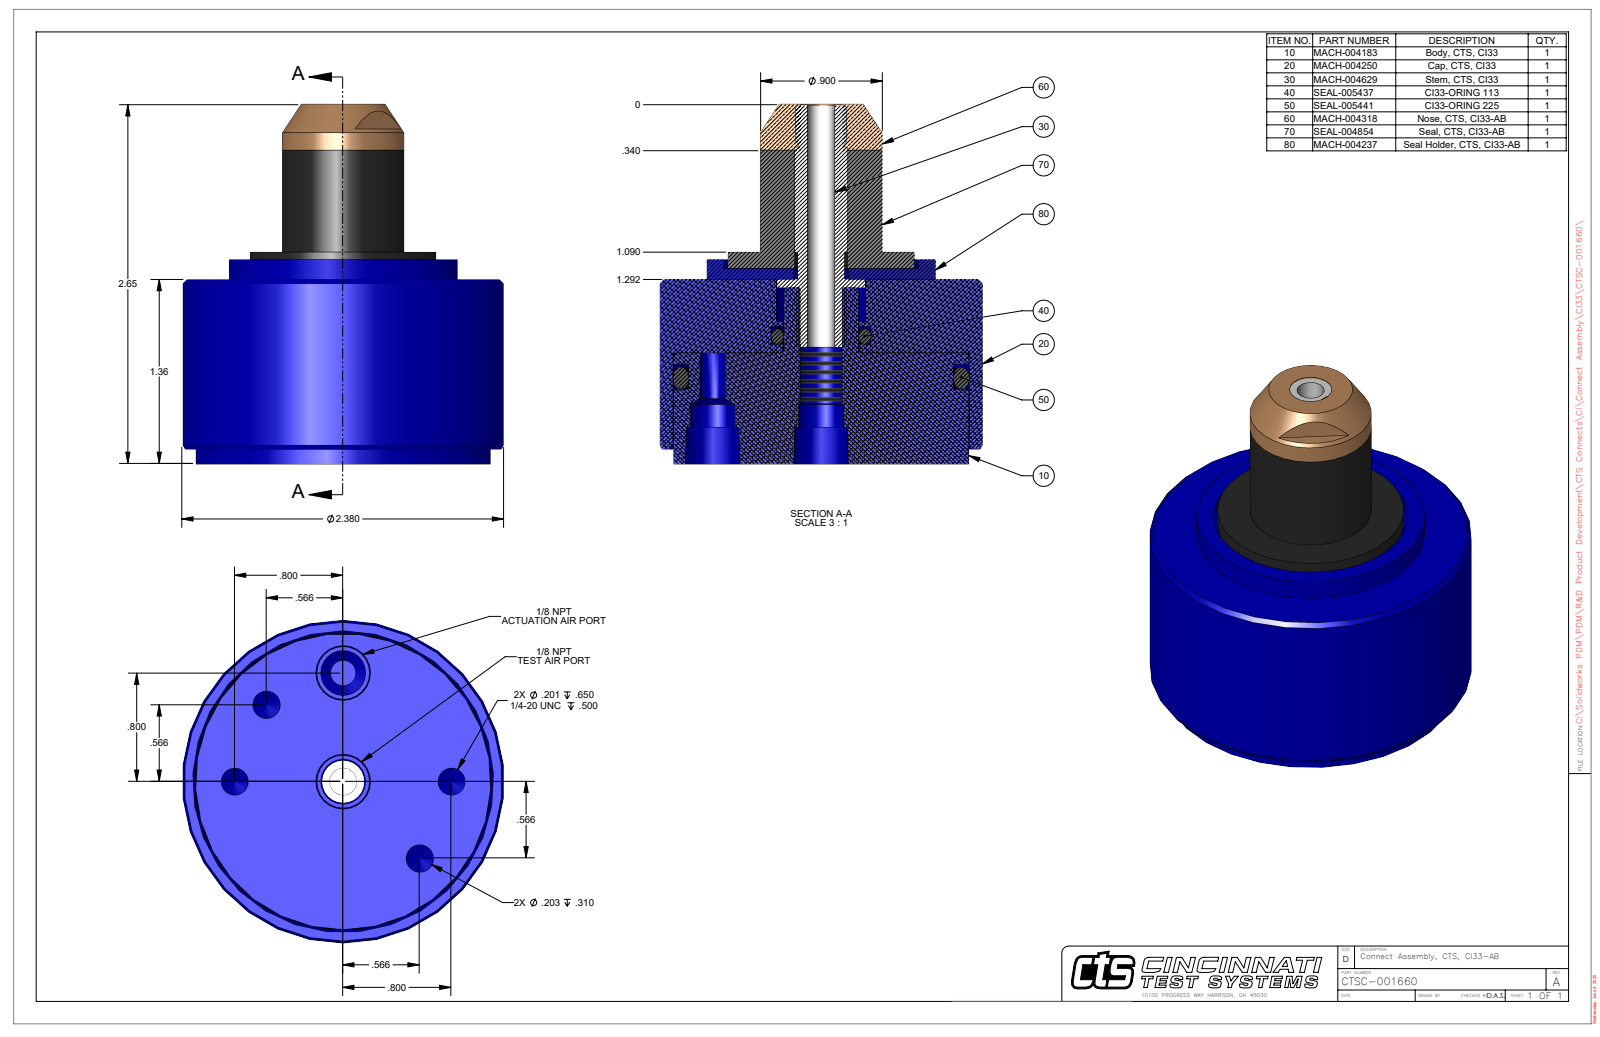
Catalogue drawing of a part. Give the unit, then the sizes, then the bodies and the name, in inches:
Units: inches
Overall size (bounding box): 2.652 × 2.38 × 2.38
Round holes (diameter × count): ⌀0.201 ×2, ⌀0.203 ×2, ⌀0.332 ×2, ⌀0.203 ×1, ⌀0.313 ×1, ⌀0.659 ×1, ⌀1.437 ×1, ⌀2.188 ×1
Round bosses / shafts (diameter × count): ⌀2.38 ×1, ⌀2.178 ×1, ⌀1.687 ×1, ⌀1.375 ×1, ⌀0.9 ×1, ⌀0.65 ×1
Main face-to-face distances: 1.36, 1.562, 0.202, 1.507, 0.147, 0.055, 0.11, 1.25, 1.397, 1.452
Hole centre spacings: 0.8, 0.612, 1.478, 1.131, 1.6
Volume: 6.787 in³ · Surface area: 31.09 in²
Bodies: 1 solid, 75 faces (21 planar, 34 cylindrical, 20 other)
Part name (STEP PRODUCT): CTSC-001660
STEP written by: SolidWorks 2023 (AUTOMOTIVE_DESIGN)
